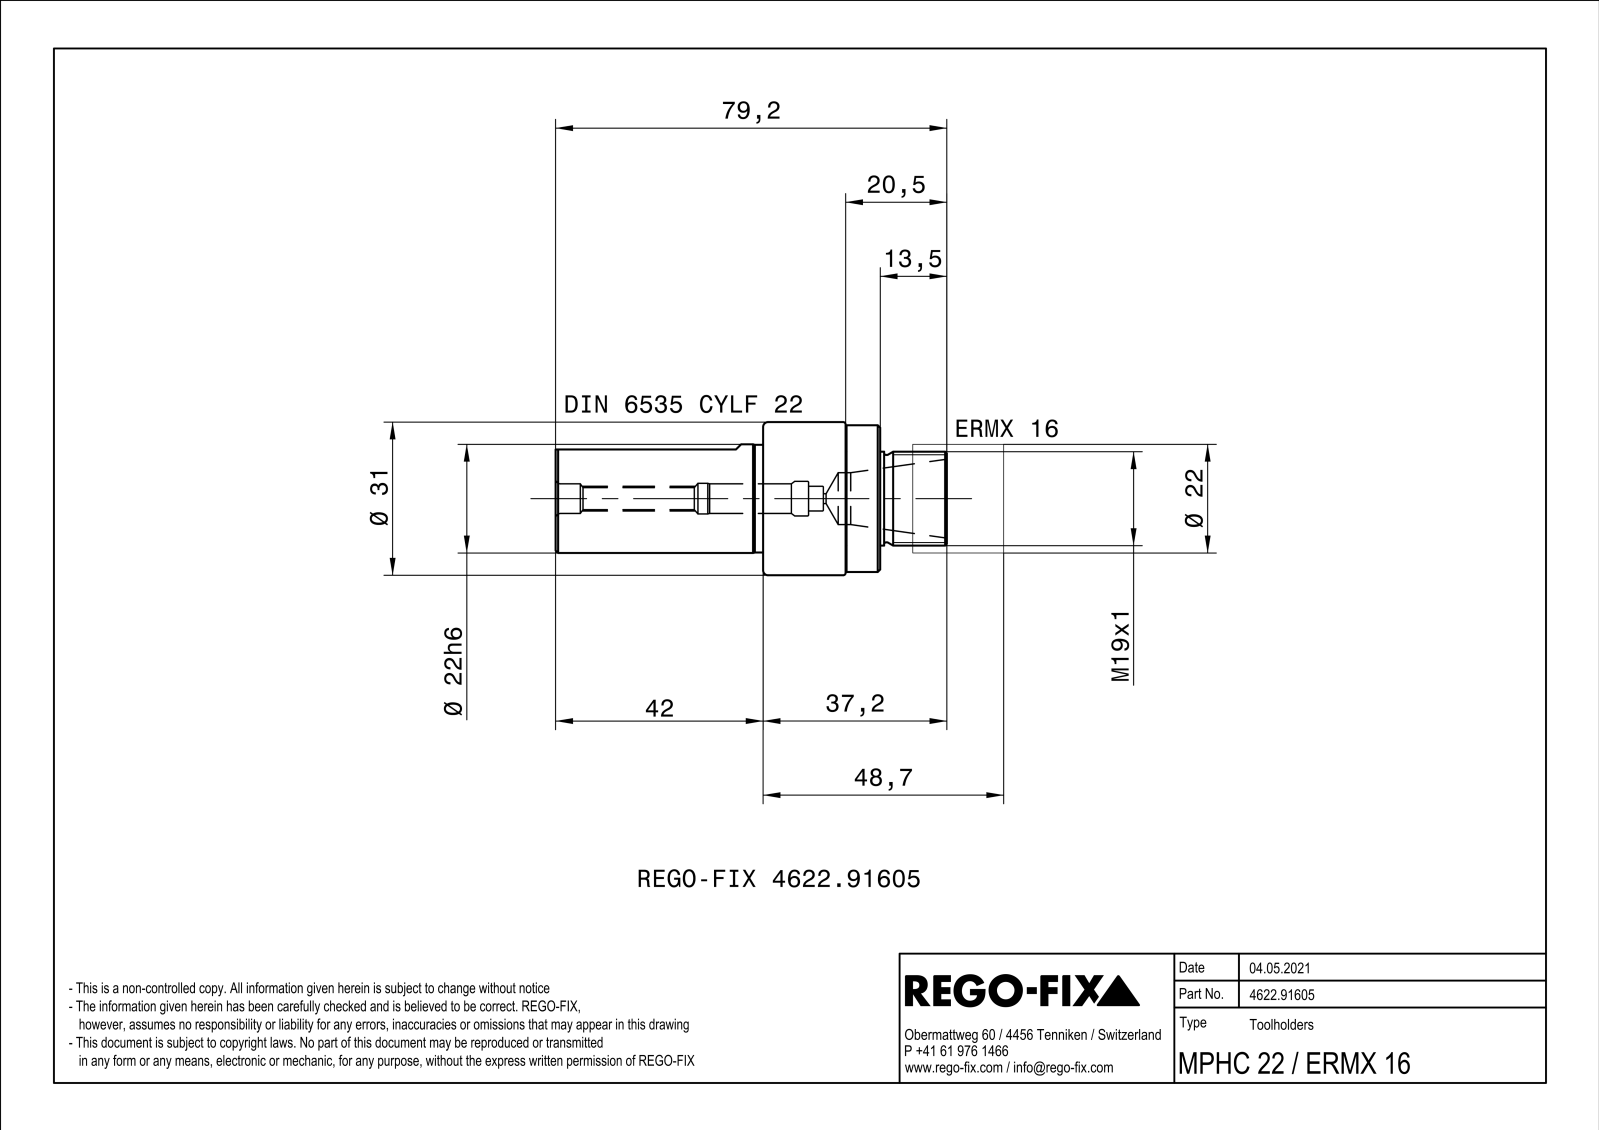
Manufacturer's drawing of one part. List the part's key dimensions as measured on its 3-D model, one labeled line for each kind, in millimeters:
Part name (STEP PRODUCT): NOCUT
STEP written by: SIEMENS PLM Software Solid Edge ST10 (AUTOMOTIVE_DESIGN)
Units: millimetres
Bodies: 6 solids, 110 faces (27 planar, 35 cylindrical, 48 other)
Overall size (bounding box): 79.2 × 31 × 31
Volume: 29 646 mm³ · Surface area: 17 024 mm²
Round holes (diameter × count): ⌀2.5 ×4, ⌀2.49 ×2, ⌀1.57 ×1, ⌀2 ×1, ⌀4.46 ×1, ⌀5 ×1, ⌀6 ×1, ⌀6.2 ×1, ⌀7 ×1, ⌀10.5 ×1, ⌀20 ×1, ⌀27 ×1
Round bosses / shafts (diameter × count): ⌀31 ×1, ⌀29.7 ×1, ⌀28 ×1, ⌀26 ×1, ⌀22 ×1, ⌀21.8 ×1, ⌀19 ×1, ⌀18.7 ×1
Main face-to-face distances: 16.7, 6, 2, 13.5, 10.7, 14.5, 7.5, 3.2, 1, 7
Hole centre spacings: 11.5, 16.26, 23
